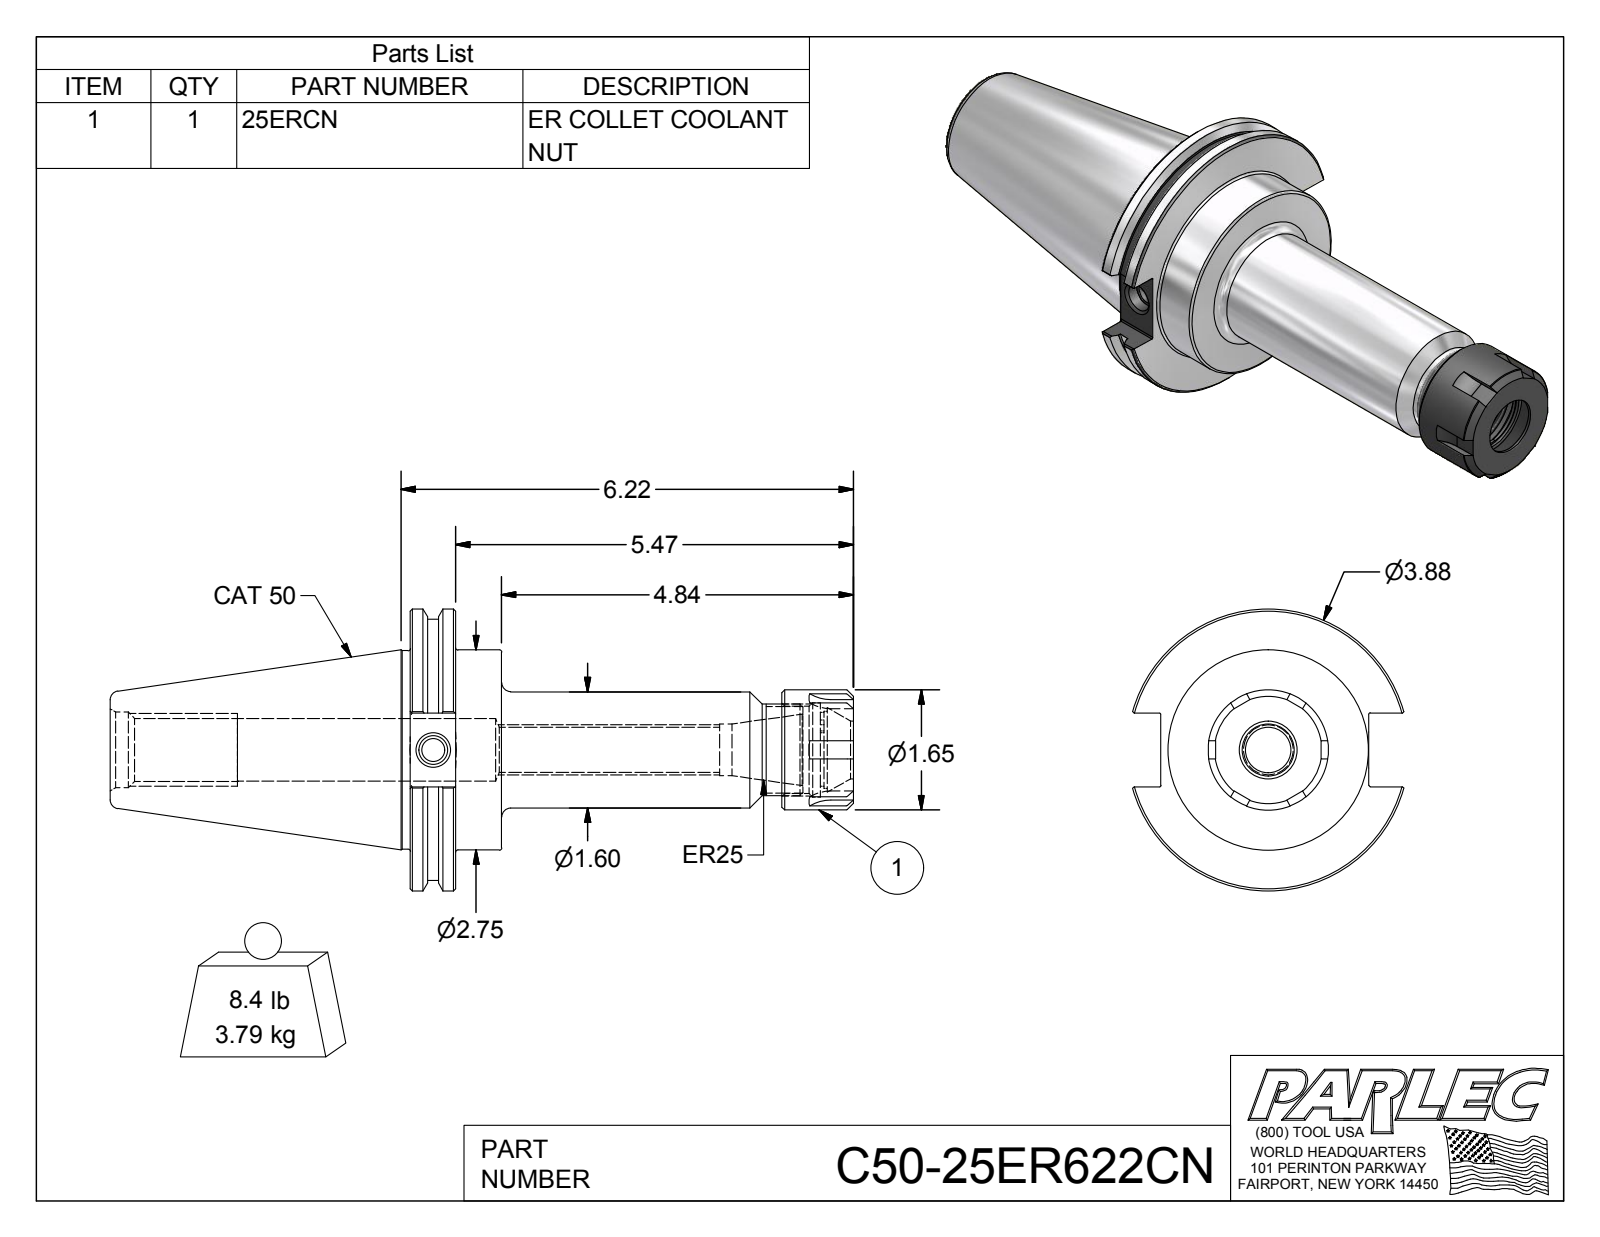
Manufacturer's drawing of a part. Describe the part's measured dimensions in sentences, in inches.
The part is named "C50-25ER622CN; C50-25ER6-1; 25ERCN". Its 3-D file was written by "Autodesk Inventor 2012 (AUTOMOTIVE_DESIGN)". It is 2 solids with 139 faces: 57 planar, 41 cylindrical and 41 other. Overall it measures 10.22 by 3.875 by 3.729 inches. Its volume is 30.09 cubic inches and its surface area 115.3 square inches. Round holes: 1 of diameter 0.315, 1 of diameter 0.399, 1 of diameter 0.62, 1 of diameter 0.71, 1 of diameter 0.794, 1 of diameter 0.864, 1 of diameter 0.865, 1 of diameter 1.038, 1 of diameter 1.057, 1 of diameter 1.201, 1 of diameter 1.294. Round bosses or shafts: 1 of diameter 3.875, 1 of diameter 3.594, 1 of diameter 2.75, 1 of diameter 2.73, 1 of diameter 1.654, 1 of diameter 1.595, 1 of diameter 1.26. Partial cylindrical surfaces (rounded edges, fillets, slot ends): 8 of radius 0.02, 6 of radius 0.5, 1 of radius 0.472, 1 of radius 0.515. The main face-to-face distances are 0.625, 1.255, 0.63, 6.095, 5.47, 4.84, 5.111, 4.486, 3.856, 0.984.
